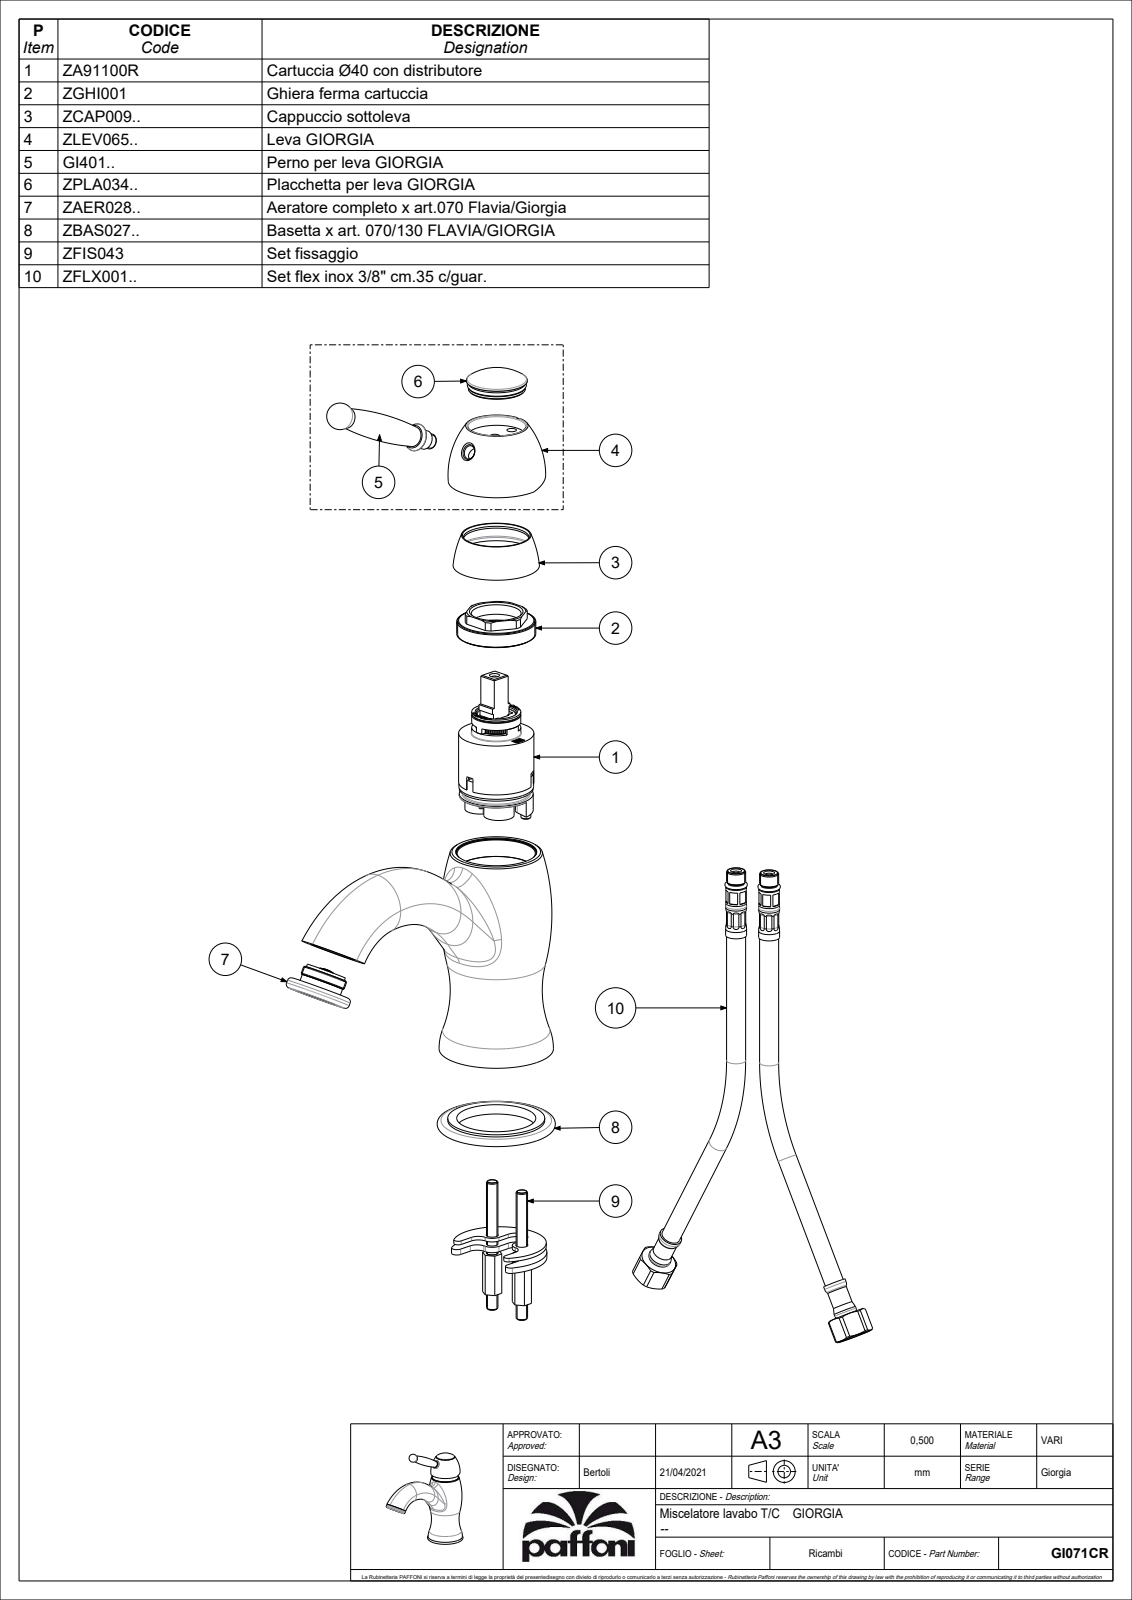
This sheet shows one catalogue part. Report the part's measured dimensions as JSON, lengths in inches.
{"part_name": "GI071CR", "step_written_by": "CREO PARAMETRIC BY PTC INC, 2020044 (CONFIG_CONTROL_DESIGN)", "units": "inches", "bodies": {"solids": 4, "faces": 2772, "planar": 2082, "cylindrical": 373, "other": 317}, "overall_size": [6.978, 6.663, 2.441], "volume_in3": 13.09, "surface_area_in2": 191.5, "round_holes": [[0.197, 5], [0.315, 4], [0.433, 3], [0.472, 3], [0.217, 2], [0.354, 2], [0.13, 1], [0.157, 1], [0.591, 1], [0.63, 1], [0.669, 1], [0.791, 1]], "round_bosses_or_shafts": [[0.626, 2], [0.37, 2], [0.335, 2], [2.004, 1], [1.929, 1], [1.555, 1], [1.543, 1], [1.528, 1]], "partial_cylinders_radius": [[0.02, 55], [0.008, 24], [0.012, 4], [0.059, 4], [0.098, 2], [0.217, 2], [0.236, 2], [0.295, 2]], "face_to_face_distances": [0.197, 0.138, 0.417, 0.157, 0.217, 0.039, 0.22, 2.283, 0.079, 0.059], "hole_center_spacings": [0.535, 0.079, 0.315, 0.339, 0.349, 0.359, 0.39, 0.402]}
